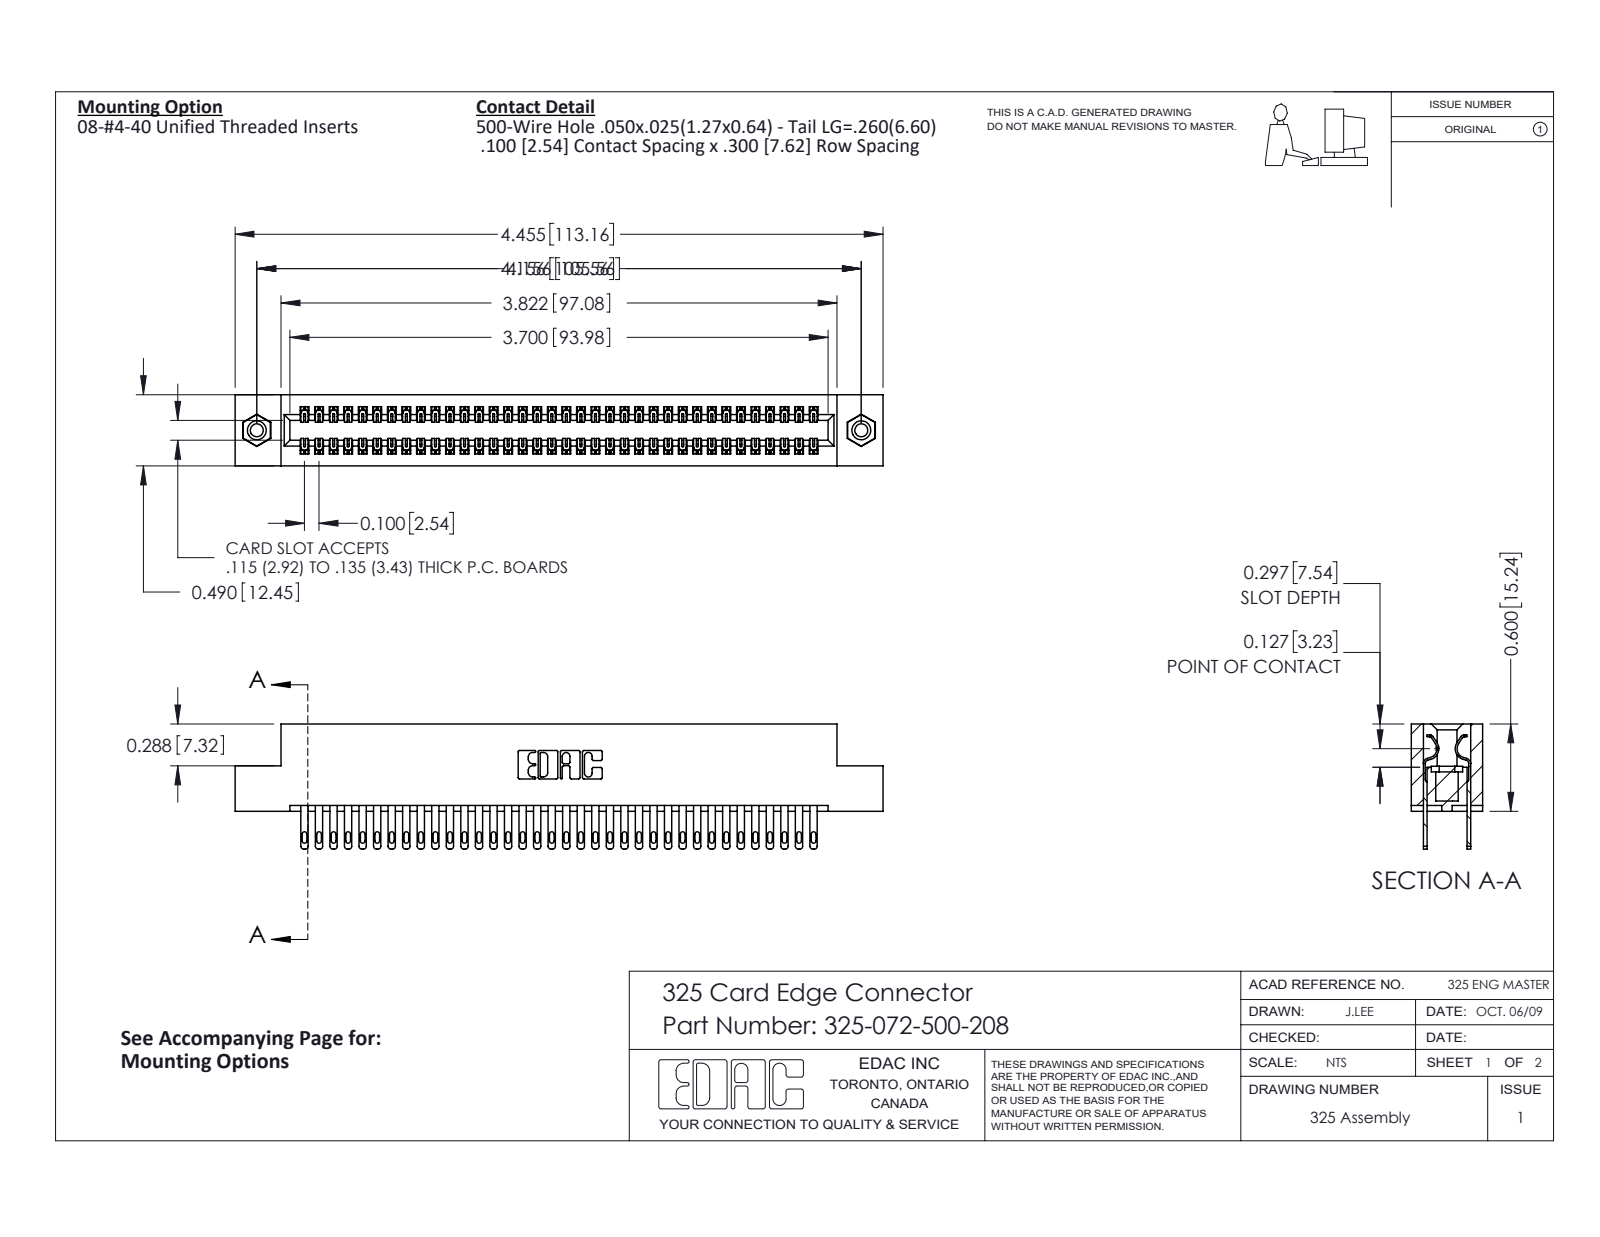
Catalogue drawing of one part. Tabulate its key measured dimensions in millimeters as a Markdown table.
| quantity | value |
| --- | --- |
| part name | 325-292-001_325-293-100; 325 Part_TI; 325-072-500-208; 345-250-001_345-250-003-102 |
| STEP written by | SolidWorks 2016 (CONFIG_CONTROL_DESIGN) |
| units | millimeters |
| bodies | 75 solids, 3630 faces (2262 planar, 1352 cylindrical, 16 other) |
| overall size | 113.2 × 21.8 × 12.4 |
| volume | 14 800 mm³ |
| surface area | 18 500 mm² |
| round holes (diameter × count) | 2.3 × 2, 3.2 × 2, 4.1 × 2 |
| round bosses / shafts (diameter × count) | 3.9 × 2 |
| partial cylindrical surfaces (radius × count) | 0.2 × 108, 0.4 × 72, 0.5 × 72, 0.3 × 22, 0.2 × 6, 0.8 × 6, 0.7 × 3, 0.4 × 2 |
| main face-to-face distances | 2.1, 10.3, 7.6, 2.7, 9.7, 0.6, 12.4, 8.3, 7, 14.2 |
| hole center spacings | 105.6 |
